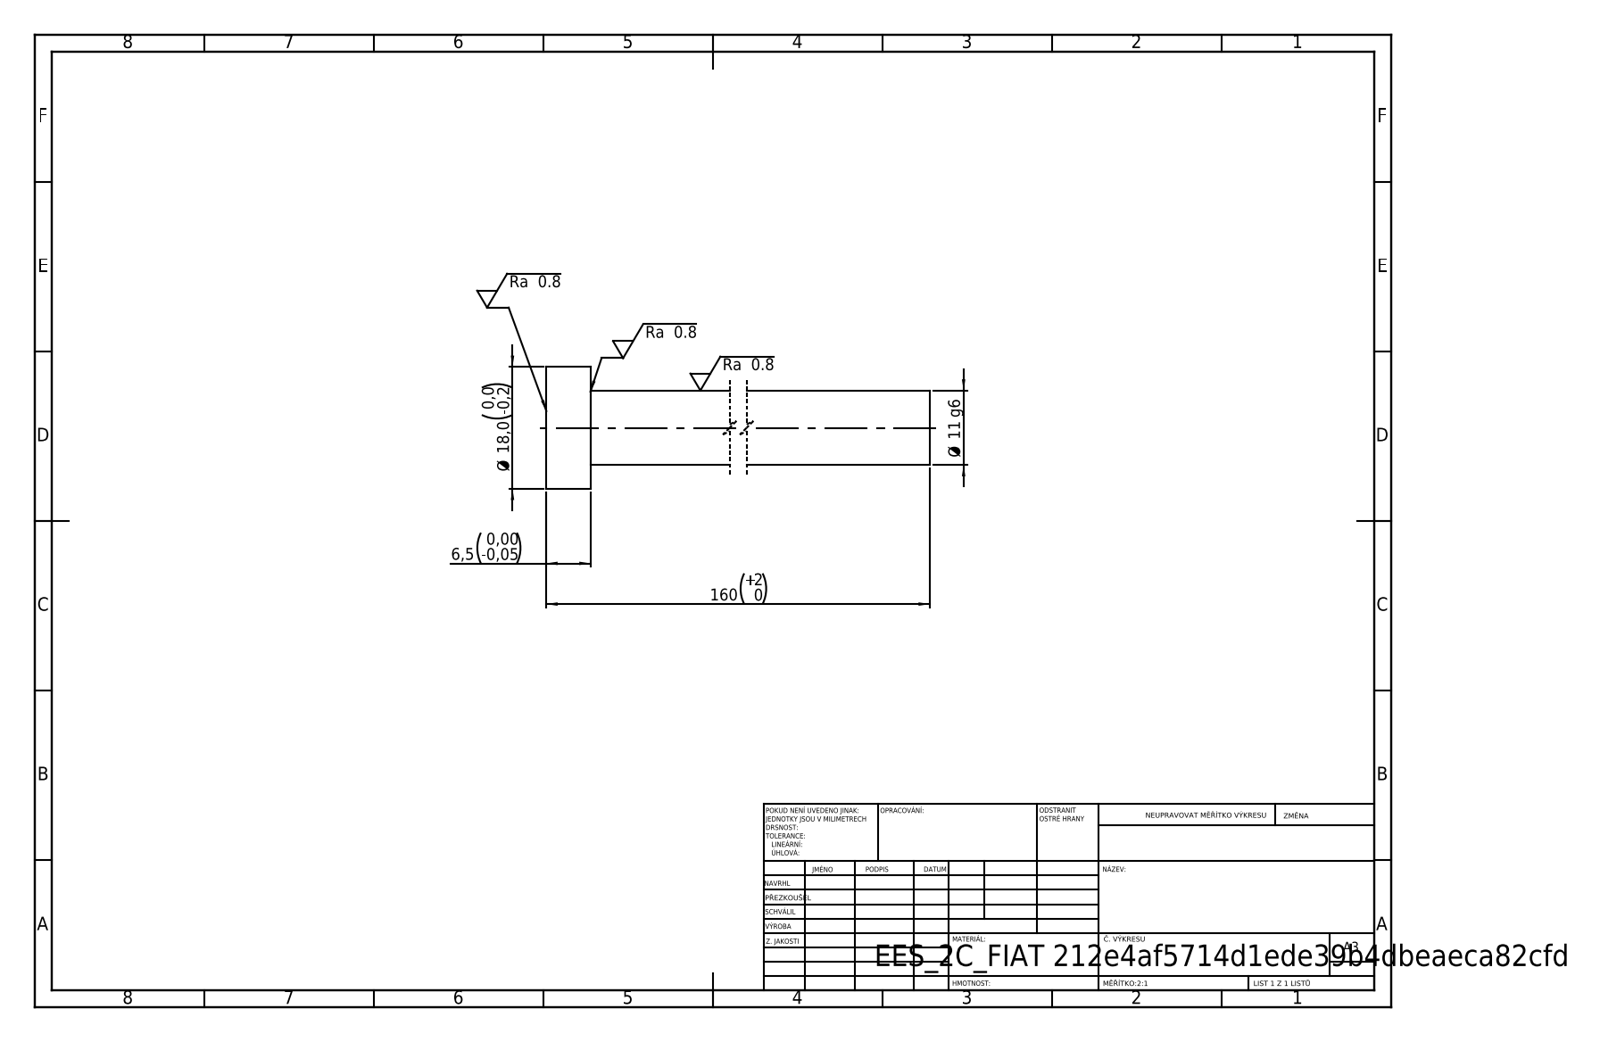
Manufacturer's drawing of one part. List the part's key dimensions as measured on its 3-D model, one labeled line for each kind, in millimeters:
STEP written by: SolidWorks 2019 (CONFIG_CONTROL_DESIGN)
Units: millimetres
Bodies: 1 solid, 7 faces (3 planar, 4 cylindrical, 0 other)
Overall size (bounding box): 160 × 18 × 18
Volume: 16 242 mm³ · Surface area: 6 181 mm²
Round bosses / shafts (diameter × count): ⌀18 ×1, ⌀11 ×1
Main face-to-face distances: 6.5, 160, 153.5
